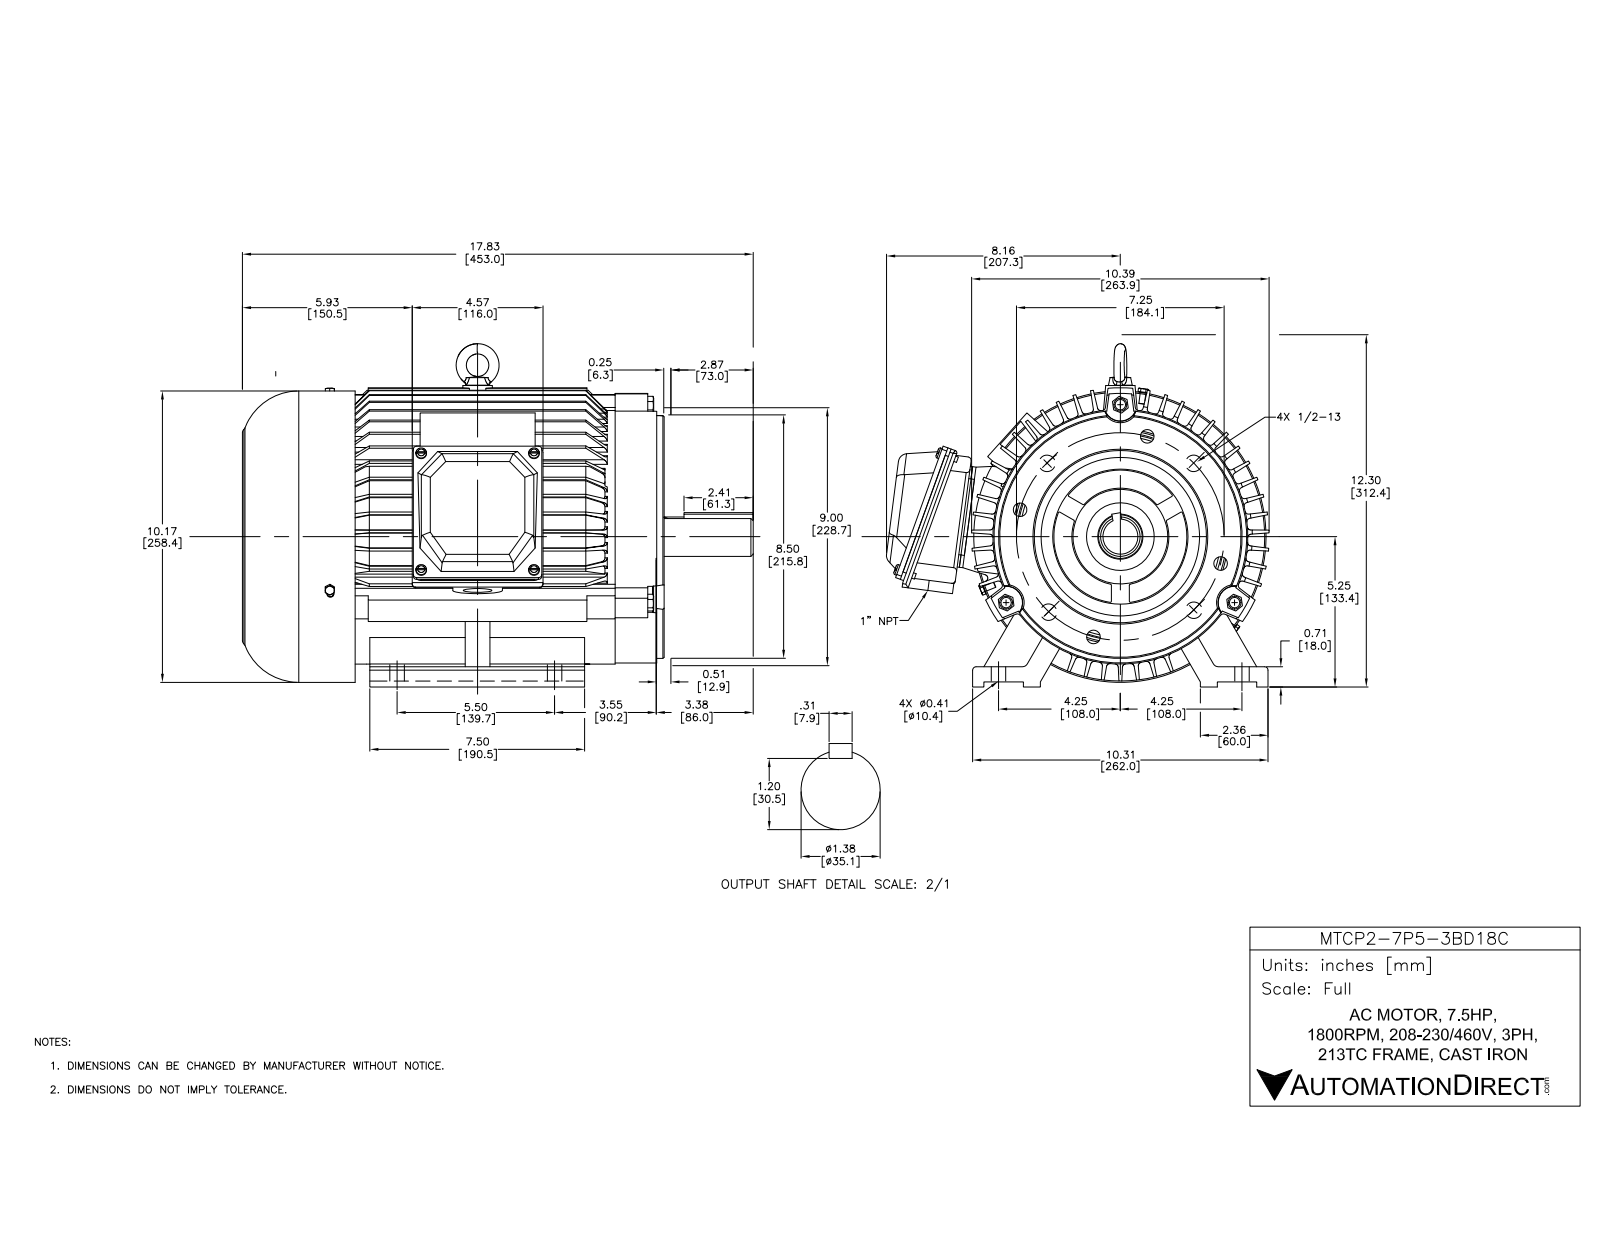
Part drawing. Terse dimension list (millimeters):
name: PEWWE-213TC fxt
written by: SolidWorks 2021 (AUTOMOTIVE_DESIGN)
unit: mm
bodies: 19 solids, 1779 faces (1021 planar, 485 cylindrical, 273 other)
size: 453 × 339.4 × 304.4
volume: 4 113 000 mm³; area: 1 235 000 mm²
holes: 8× ⌀5.8, 6× ⌀5, 4× ⌀4.2, 4× ⌀6, 4× ⌀7, 4× ⌀10.7, 4× ⌀11, 3× ⌀8, 3× ⌀10, 3× ⌀13.7, 1× ⌀8.5, 1× ⌀11.5
bosses: 7× ⌀5, 3× ⌀12, 2× ⌀10.9, 1× ⌀258.4, 1× ⌀256, 1× ⌀226, 1× ⌀224, 1× ⌀215.9
rounds: 93× R3, 32× R1.3, 16× R7, 12× R1, 9× R1.5, 6× R2.3, 6× R11, 4× R2
face distances: 18, 4, 1.2, 371.2, 372.4, 4.5, 13.5, 16.3, 354.9, 356.2
hole spacings: 100, 68, 110, 148.7, 68, 96.2, 110, 148.7
